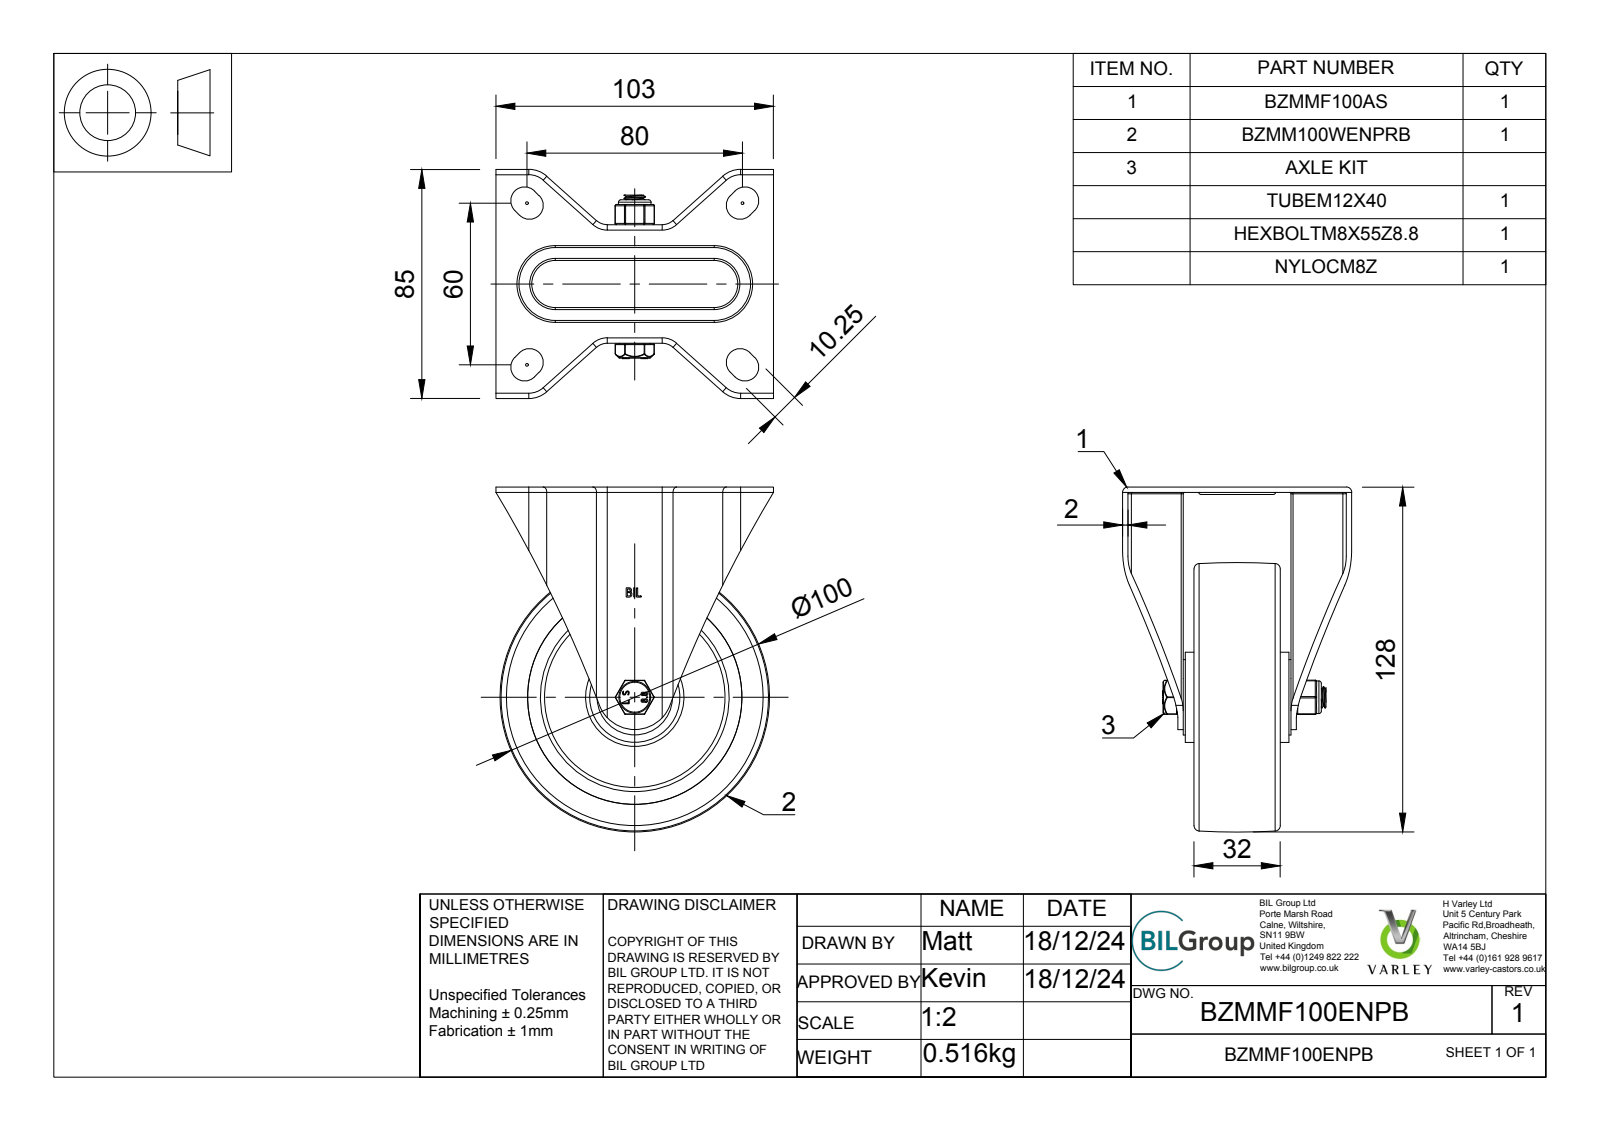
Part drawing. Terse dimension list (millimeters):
name: BZMMF100ENPB v3; BZMMF100AS v1; BZMMF100AS; ZINC PLATED, PRESSED STEEL BRACKET (+8 more)
written by: Autodesk Translation Framework v13.20.0.188 (AP242_MANAGED_MODEL_BASED_3D_ENGINEERING_MIM_LF)
unit: mm
bodies: 17 solids, 491 faces (197 planar, 198 cylindrical, 96 other)
size: 128 × 103 × 85
volume: 209 006 mm³; area: 103 903 mm²
holes: 2× ⌀0.66, 1× ⌀8, 1× ⌀8.25, 1× ⌀8.4, 1× ⌀8.6, 1× ⌀12.5, 1× ⌀13, 1× ⌀20, 1× ⌀22.1, 1× ⌀70, 1× ⌀79.5
bosses: 8× ⌀4, 1× ⌀33.5, 1× ⌀28, 1× ⌀22, 1× ⌀19.5, 1× ⌀12.1, 1× ⌀11.9, 1× ⌀11.5
rounds: 26× R0.5, 12× R0.25, 8× R0.75, 8× R2, 8× R5.12, 4× R0.33, 4× R0.64, 4× R3
face distances: 2, 18, 4, 14.26, 36, 22, 14, 20, 38, 6
hole spacings: 3.22, 2.49
